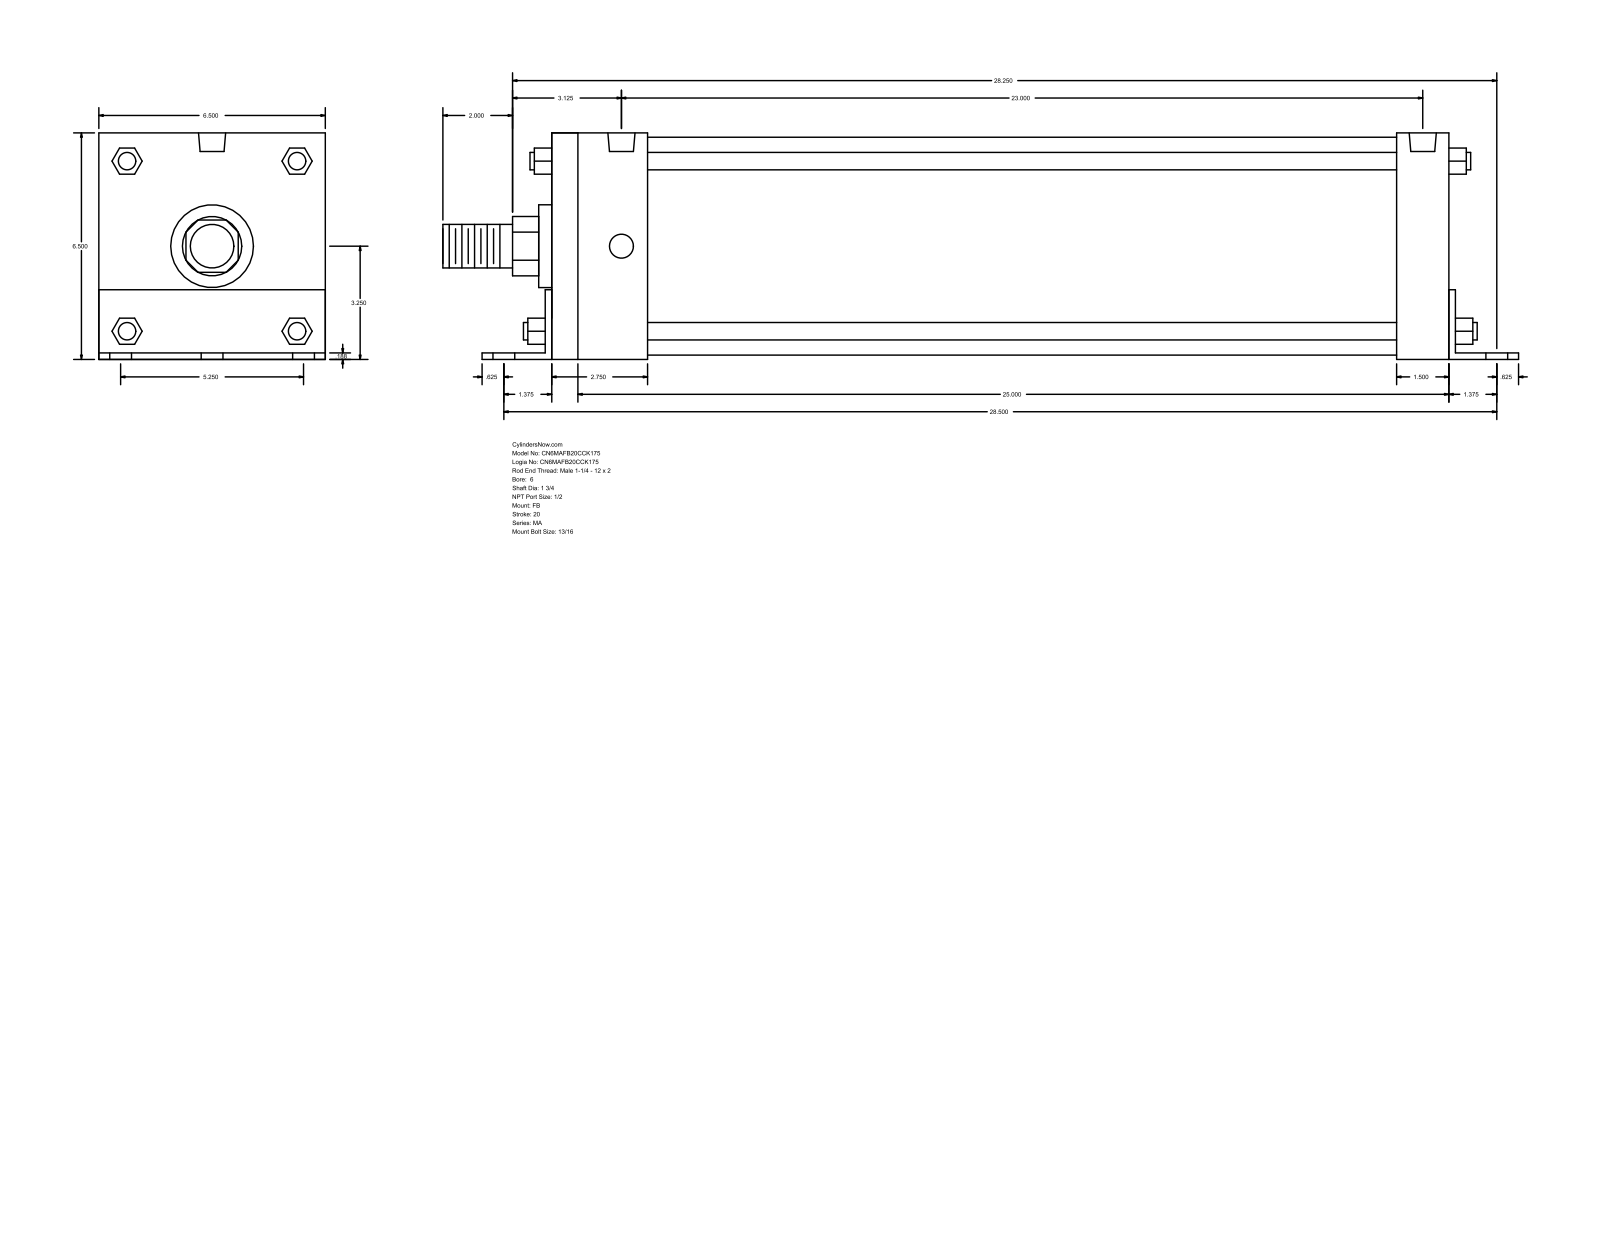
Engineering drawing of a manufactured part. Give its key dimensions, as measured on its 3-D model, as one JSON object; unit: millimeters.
{"part_name": "MA_FB__0600_1.75", "step_written_by": "GSSL Pune (CONFIG_CONTROL_DESIGN)", "units": "millimeters", "bodies": {"solids": 0, "faces": 140, "planar": 105, "cylindrical": 35, "other": 0}, "overall_size": [784.23, 165.15, 165.1], "round_holes": [[20.64, 6], [17.46, 4], [19.77, 2]], "round_bosses_or_shafts": [[12.7, 4], [158.75, 1], [60.33, 1], [44.45, 1], [31.75, 1]], "partial_cylinders_radius": [[21.63, 1], [32.05, 1]], "face_to_face_distances": [165.1, 4.76, 654.05, 165.15, 4.71, 160.39, 69.85, 74.61, 38.1, 4.77], "hole_center_spacings": [66.67, 726.96, 723.9, 85.78, 108.6, 133.34, 584.2, 641.64]}
